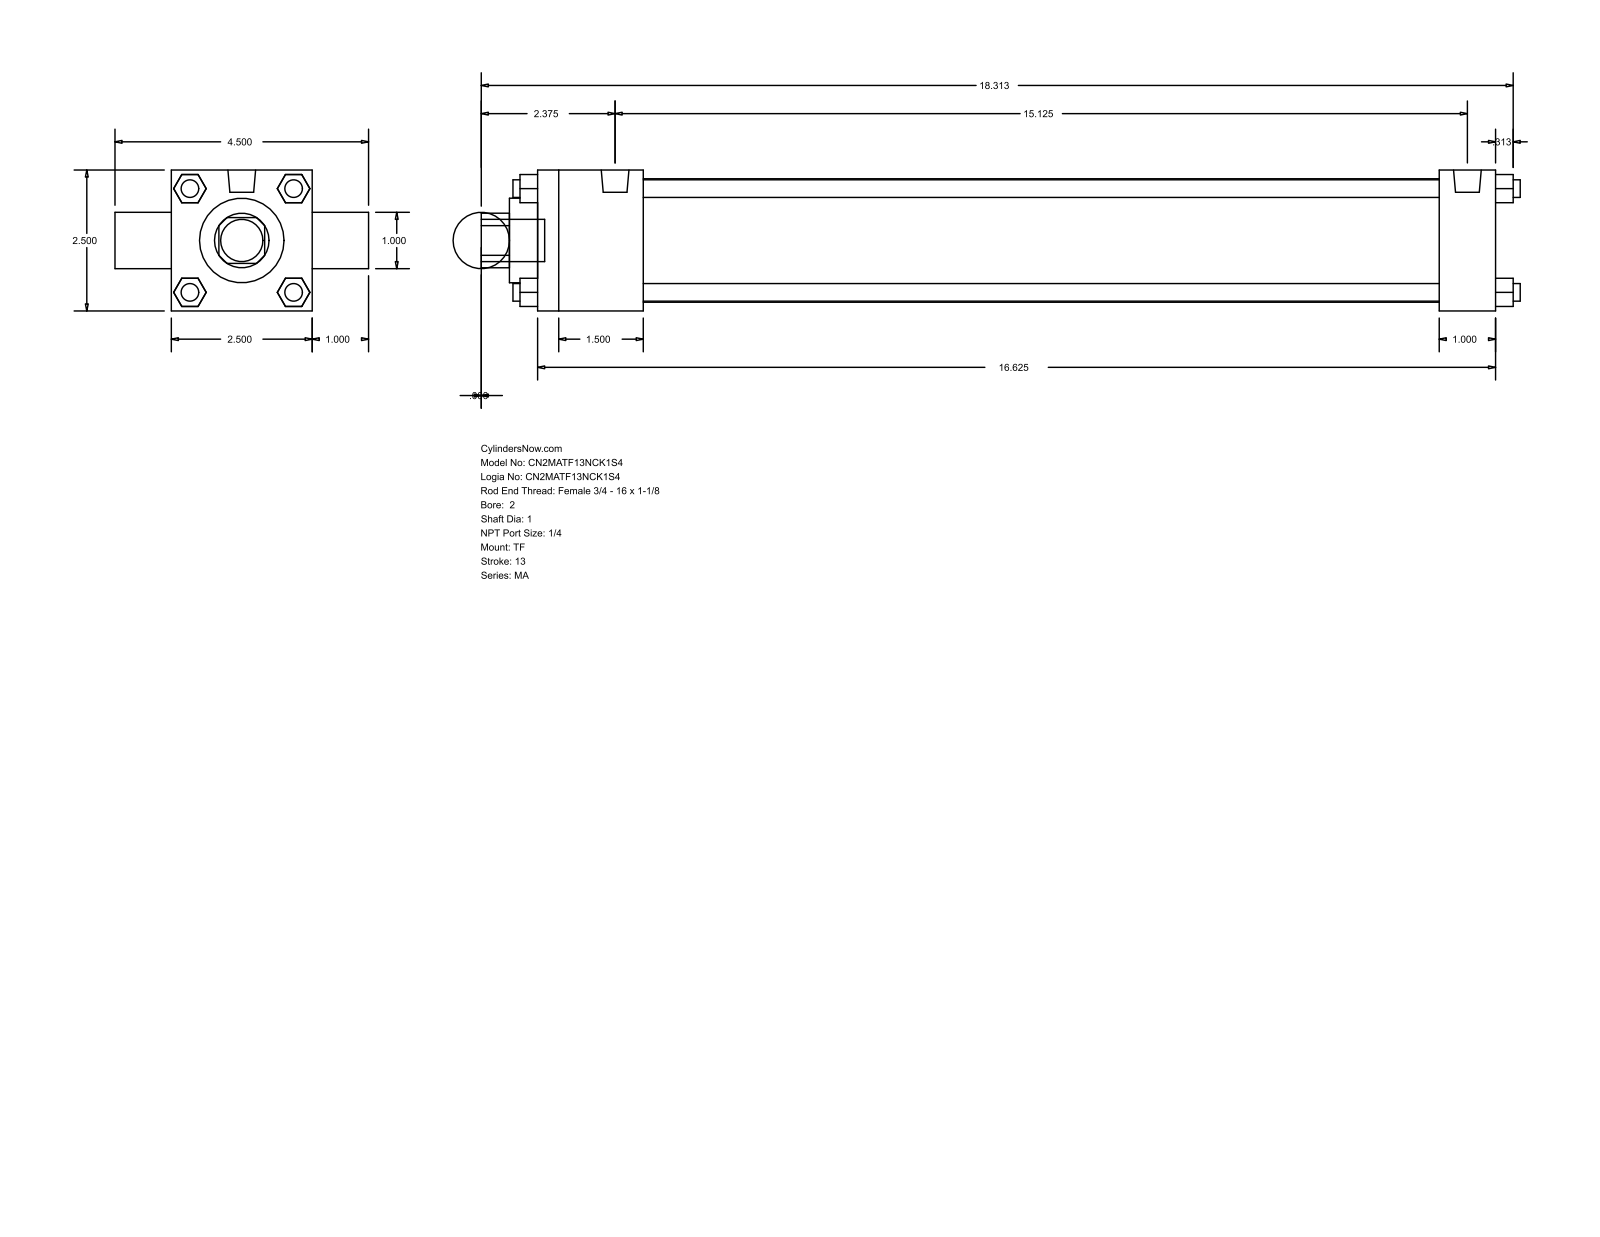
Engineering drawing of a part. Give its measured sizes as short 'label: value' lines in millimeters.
name: MA_TF__0200_1
written by: GSSL Pune (CONFIG_CONTROL_DESIGN)
unit: mm
bodies: 0 solids, 120 faces (92 planar, 28 cylindrical, 0 other)
size: 468.31 × 114.3 × 63.5
holes: 2× ⌀25.4, 1× ⌀38.1, 1× ⌀55.63
bosses: 7× ⌀7.94, 2× ⌀12.49, 1× ⌀19.05
rounds: 1× R12.29
face distances: 63.5, 25.4, 431.8, 12.7, 47.63, 406.4, 358.77, 384.17, 88.9, 23.37
